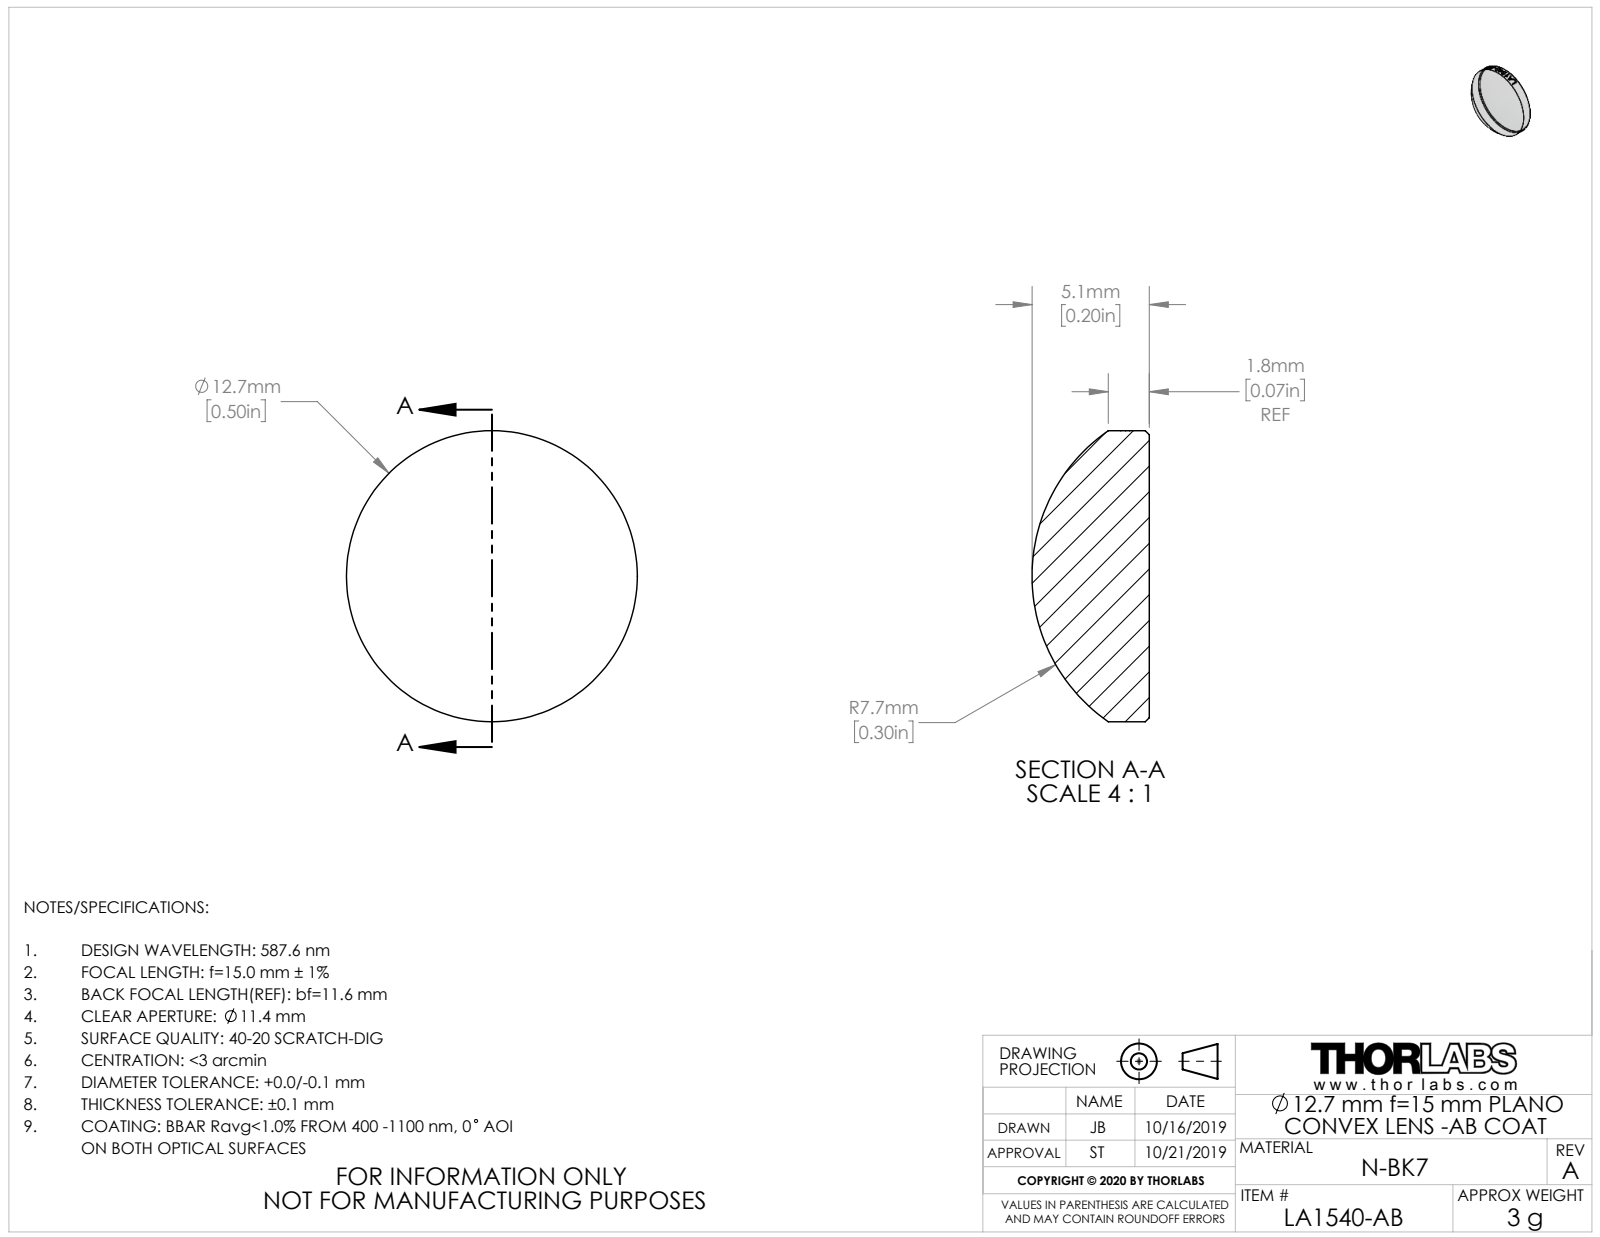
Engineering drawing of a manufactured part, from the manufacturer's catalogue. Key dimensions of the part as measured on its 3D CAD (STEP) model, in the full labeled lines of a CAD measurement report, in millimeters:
Part name (STEP PRODUCT): TTN195790-E0W
STEP written by: SolidWorks 2018 (CONFIG_CONTROL_DESIGN)
Units: millimetres
Bodies: 1 solid, 23 faces (1 planar, 18 cylindrical, 4 other)
Overall size (bounding box): 12.7 × 12.7 × 5.1
Volume: 460 mm³ · Surface area: 355 mm²
Round bosses / shafts (diameter × count): ⌀12.7 ×1
